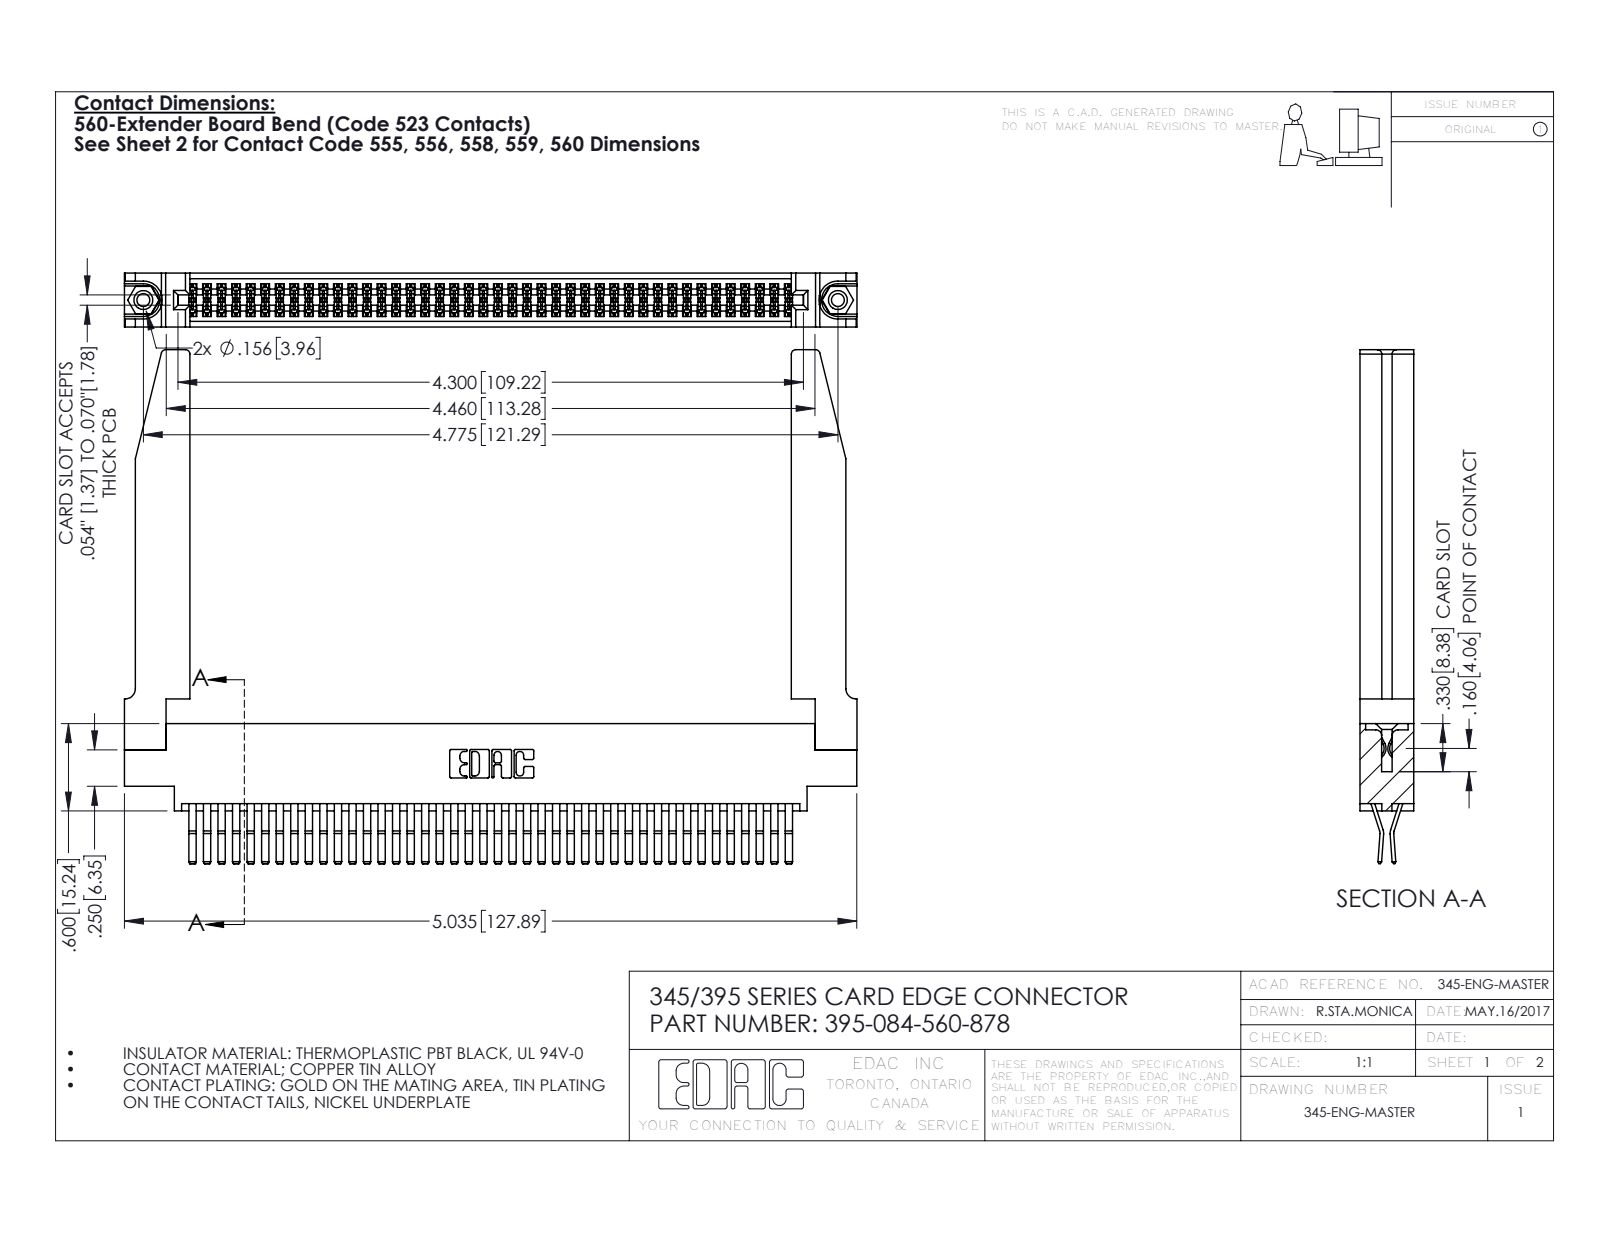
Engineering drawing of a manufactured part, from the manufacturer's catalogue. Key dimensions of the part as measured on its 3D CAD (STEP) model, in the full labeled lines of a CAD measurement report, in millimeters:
Part name (STEP PRODUCT): 395-084-560-878; 345 Part_0.170 Offset - 0.156 Dia-TH; 345-250-001_345-250-001-102; 345-220-078_345-220-078 (+1 more)
STEP written by: SolidWorks 2016 (CONFIG_CONTROL_DESIGN)
Units: millimetres
Bodies: 89 solids, 4732 faces (2998 planar, 1682 cylindrical, 52 other)
Overall size (bounding box): 127.9 × 89.7 × 9.4
Volume: 20 630 mm³ · Surface area: 27 410 mm²
Round holes (diameter × count): ⌀2.3 ×2, ⌀3.2 ×2, ⌀4 ×2, ⌀1.6 ×1
Round bosses / shafts (diameter × count): ⌀3.9 ×2
Partial cylindrical surfaces — rounded edges, fillets, slot ends (radius × count): R0.2 ×127, R0.3 ×22, R0.8 ×8, R0.2 ×6, R0.8 ×6, R0.7 ×3, R0.3 ×2, R0.4 ×2
Main face-to-face distances: 9.4, 1.8, 7.6, 0.6, 2.5, 6.9, 5.1, 5.7, 4.4, 3.8
Hole centre spacings: 6.9, 115.3, 121.3
